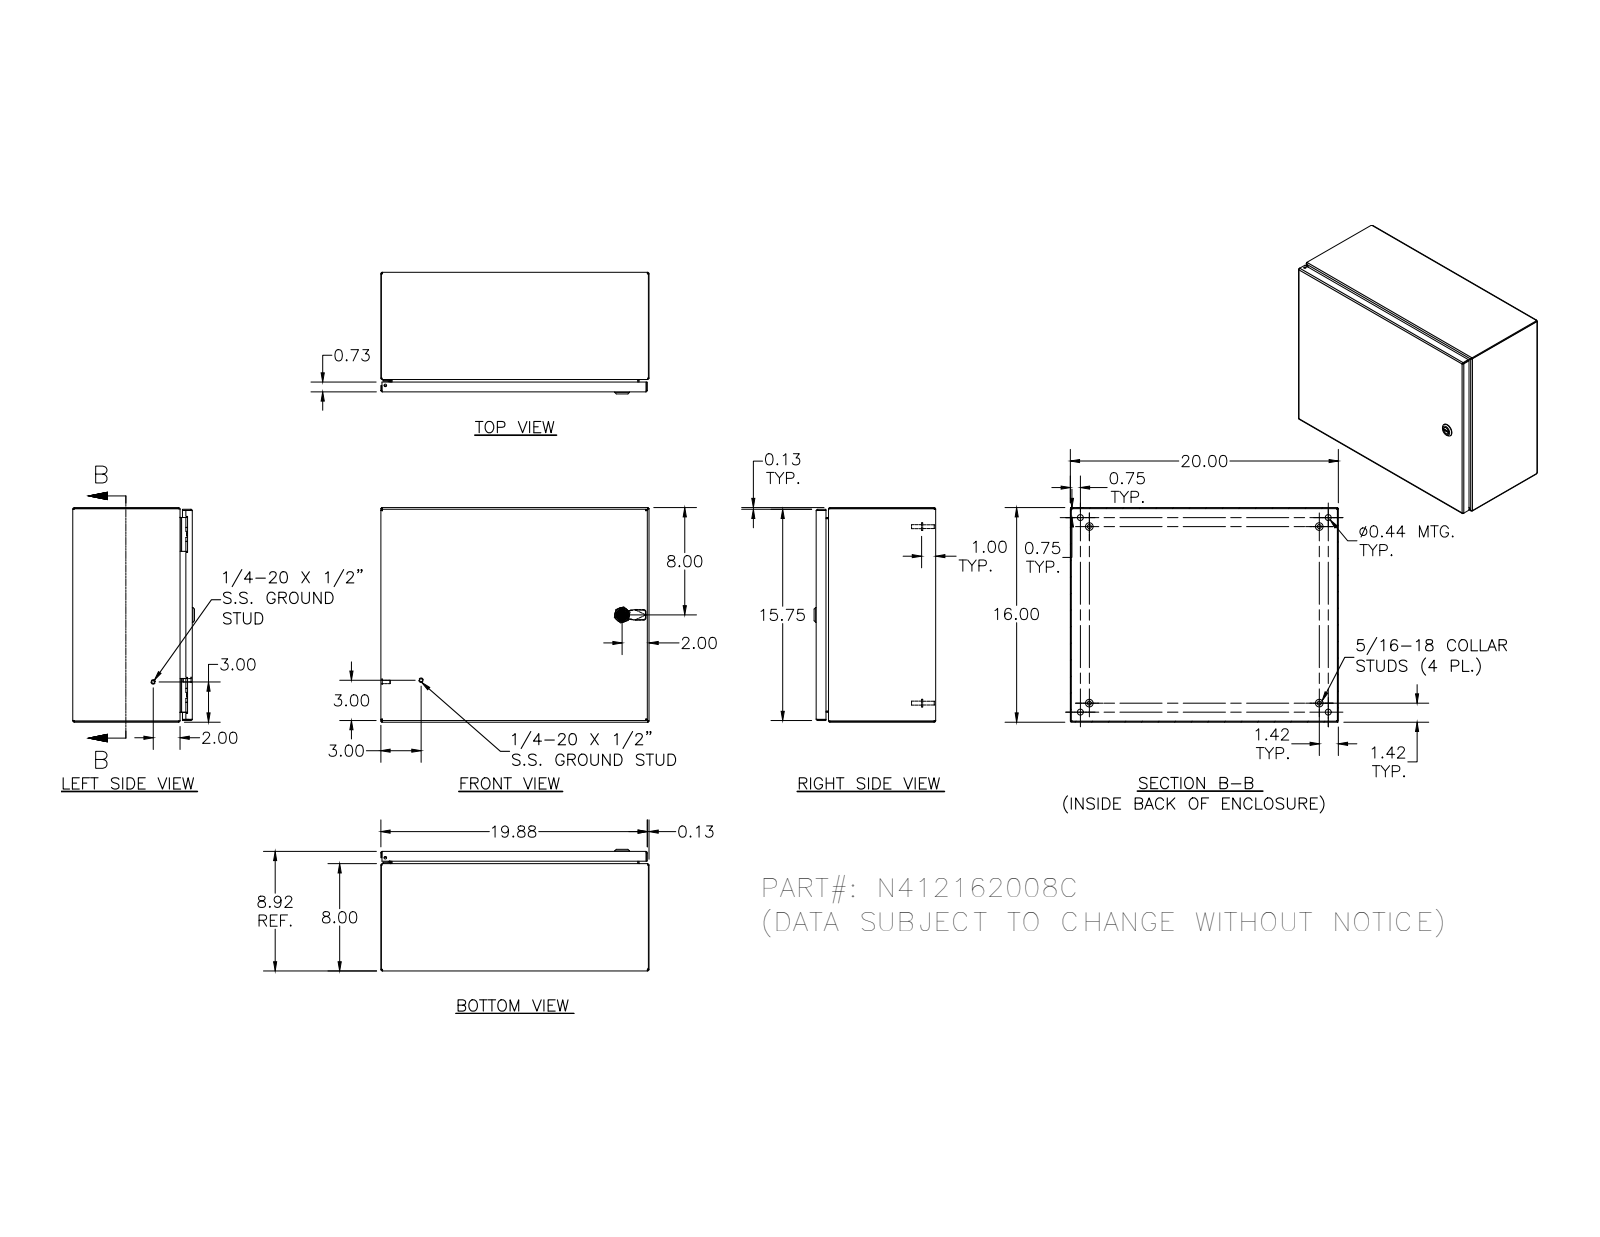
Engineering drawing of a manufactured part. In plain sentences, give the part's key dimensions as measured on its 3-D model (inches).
The part is named "N412162008C". Its 3-D file was written by "SolidWorks 2018 (AUTOMOTIVE_DESIGN)". It is 33 solids with 1449 faces: 530 planar, 547 cylindrical and 372 other. Overall it measures 20 by 16 by 9.075 inches. Its volume is 101 cubic inches and its surface area 2 748 square inches. Round holes: 5 of diameter 0.188, 4 of diameter 0.093, 4 of diameter 0.152, 4 of diameter 0.167, 4 of diameter 0.172, 4 of diameter 0.437, 2 of diameter 0.156, 1 of diameter 0.187, 1 of diameter 0.197, 1 of diameter 0.315, 1 of diameter 0.394, 1 of diameter 0.402. Round bosses or shafts: 10 of diameter 0.25, 4 of diameter 0.563, 4 of diameter 0.36, 4 of diameter 0.32, 4 of diameter 0.3, 4 of diameter 0.275, 4 of diameter 0.256, 4 of diameter 0.164. Partial cylindrical surfaces (rounded edges, fillets, slot ends): 30 of radius 0.012, 30 of radius 0.031, 26 of radius 0.05, 20 of radius 0.105, 18 of radius 0.016, 16 of radius 0.125, 13 of radius 0.02, 8 of radius 0.032. The main face-to-face distances are 0.074, 8.843, 8.769, 8.917, 0.074, 15.926, 16, 15.852, 15.926, 19.926. The hole center spacings are 12, 0.66, 0.656, 1.307, 1.965, 11.34, 11.996, 12.656.
